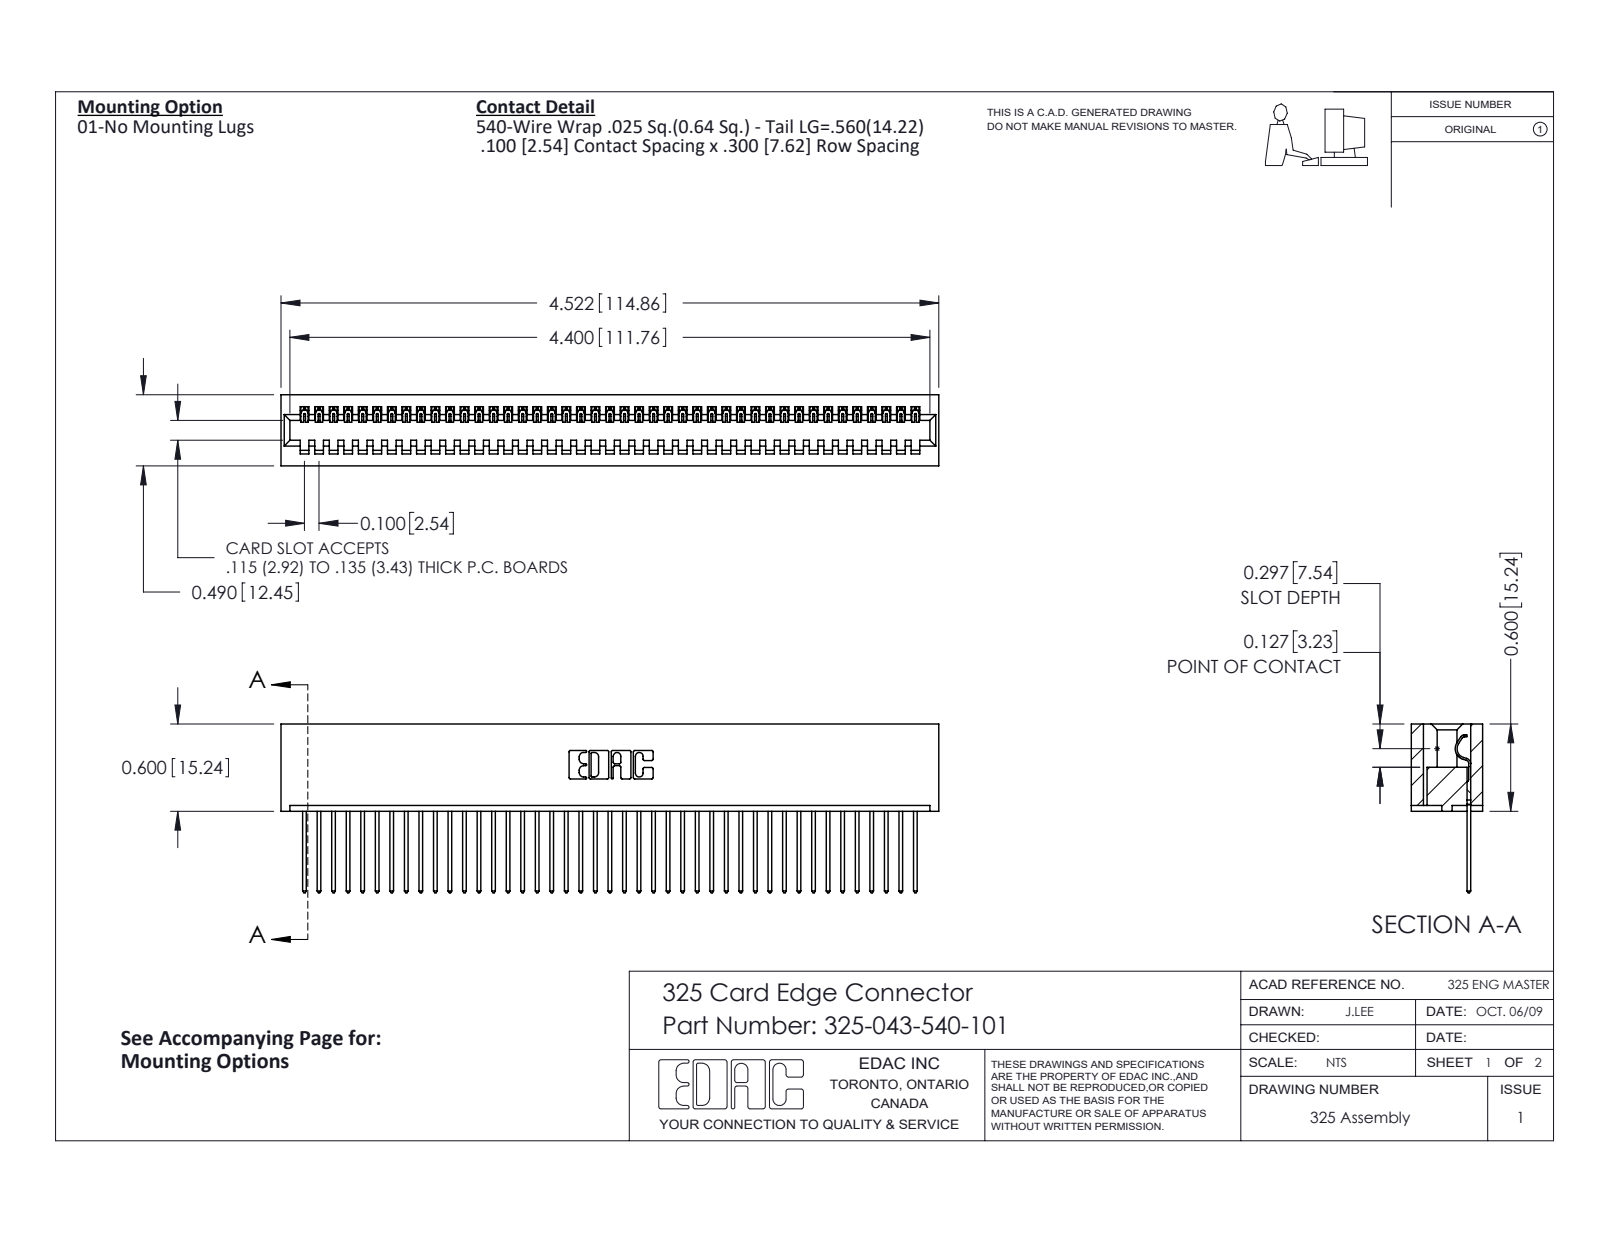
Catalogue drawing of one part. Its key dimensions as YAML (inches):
part_name: "325-292-001_325-293-140; 325-043-540-101; 325 Part_Lugless"
step_written_by: "SolidWorks 2016 (CONFIG_CONTROL_DESIGN)"
units: inches
bodies: {solids: 44, faces: 2600, planar: 1872, cylindrical: 728, other: 0}
overall_size: [4.522, 1.16, 0.49]
volume: 0.929
surface_area: 27.23
partial_cylinders:
  - {radius: 0.006, count: 86}
  - {radius: 0.01, count: 86}
  - {radius: 0.01, count: 22}
  - {radius: 0.007, count: 6}
  - {radius: 0.031, count: 6}
  - {radius: 0.026, count: 3}
  - {radius: 0.014, count: 1}
  - {radius: 0.022, count: 1}
face_to_face_distances: [0.083, 0.407, 0.49, 0.3, 0.107, 0.383, 0.025, 0.325, 0.56, 0.263]
